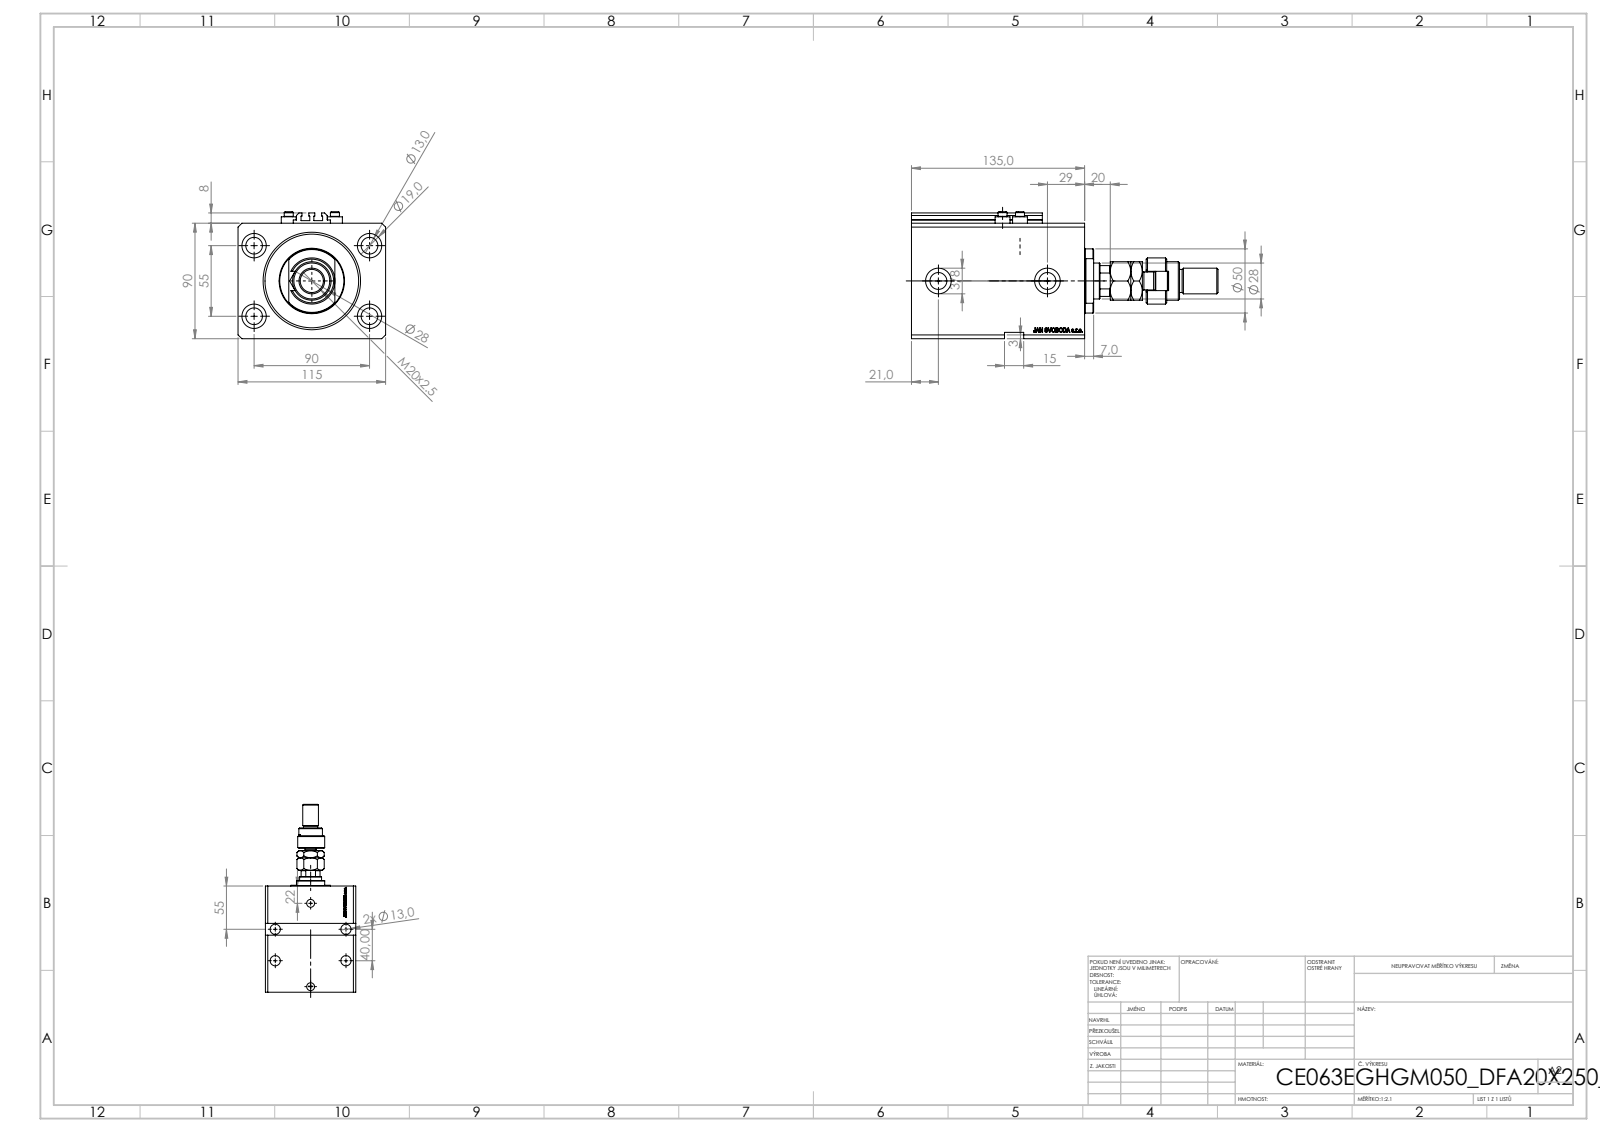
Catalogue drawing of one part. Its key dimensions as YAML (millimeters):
part_name: "MFA; FEMALE_PART_FOR_DFA; ALLEN BOLT V250CE; V250CE_E_Body (+2 more)"
step_written_by: "SolidWorks 2019 (CONFIG_CONTROL_DESIGN)"
units: millimeters
bodies: {solids: 10, faces: 1212, planar: 571, cylindrical: 159, other: 482}
overall_size: [239, 115, 99]
volume: 1208000
surface_area: 199899
round_holes:
  - {diameter: 13, count: 8}
  - {diameter: 1.25, count: 4}
  - {diameter: 4, count: 4}
  - {diameter: 19, count: 4}
  - {diameter: 10, count: 2}
  - {diameter: 13.16, count: 2}
  - {diameter: 20, count: 2}
  - {diameter: 18.5, count: 1}
  - {diameter: 28, count: 1}
  - {diameter: 63, count: 1}
  - {diameter: 76, count: 1}
round_bosses_or_shafts:
  - {diameter: 11.6, count: 4}
  - {diameter: 7, count: 4}
  - {diameter: 50, count: 1}
  - {diameter: 36, count: 1}
  - {diameter: 30, count: 1}
  - {diameter: 22, count: 1}
  - {diameter: 20, count: 1}
  - {diameter: 18, count: 1}
partial_cylinders:
  - {radius: 0.2, count: 10}
  - {radius: 7.5, count: 1}
  - {radius: 12, count: 1}
  - {radius: 13.5, count: 1}
face_to_face_distances: [115, 90, 20, 135, 17.9, 117.1, 97.1, 65, 30, 47.1]
hole_center_spacings: [52.74, 55.8, 85.76, 90, 13.6, 27.39, 28.46, 33.62]
